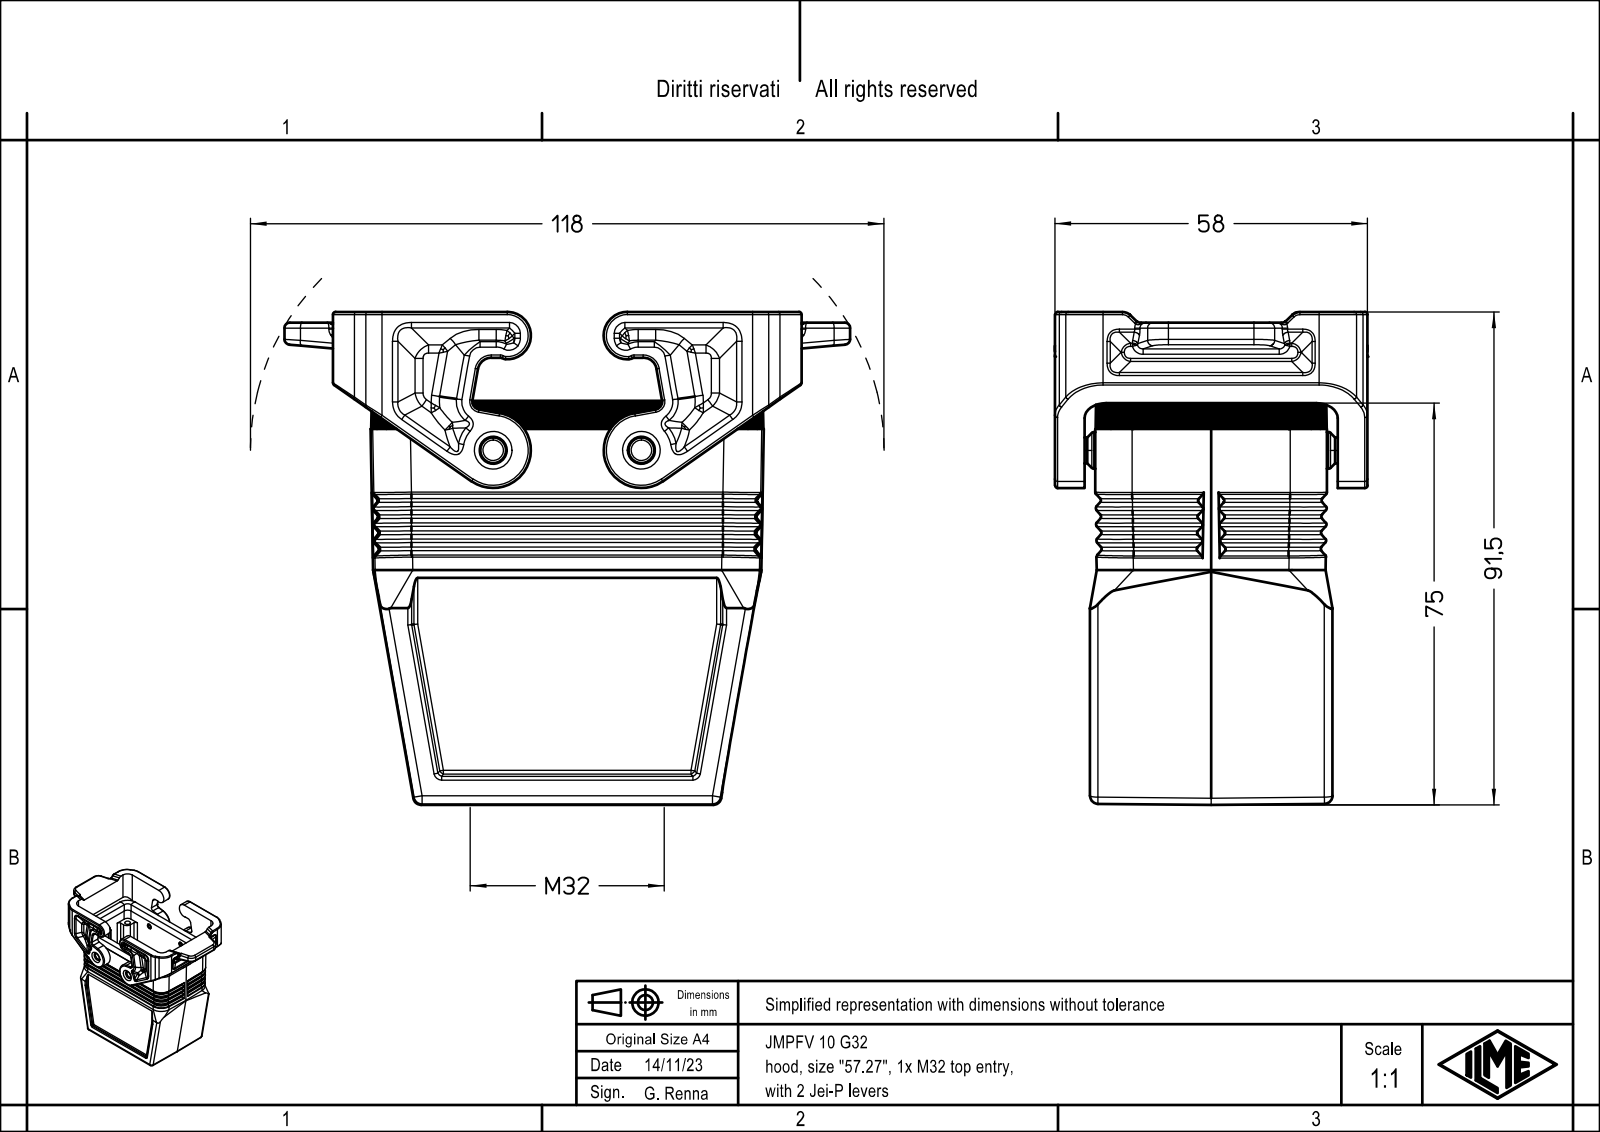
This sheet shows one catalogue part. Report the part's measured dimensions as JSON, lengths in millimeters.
{"part_name": "JMPFV 10 G32", "step_written_by": "Creo Elements/Direct Modeling 20.1B 02-Apr-2019 (C) Parametric Technology GmbH (AUTOMOTIVE_DESIGN)", "units": "millimeters", "bodies": {"solids": 1, "faces": 1097, "planar": 270, "cylindrical": 349, "other": 478}, "overall_size": [105, 91.45, 58.08], "volume_mm3": 96180, "surface_area_mm2": 47623, "round_holes": [[3, 4], [3.5, 4], [4.8, 2], [30.6, 1]], "round_bosses_or_shafts": [[6.8, 2]], "partial_cylinders_radius": [[0.5, 69], [1, 56], [3, 34], [1.5, 28], [2, 20], [0.33, 15], [7, 14], [4, 12]], "face_to_face_distances": [39.25, 2, 3.75, 5.75, 1, 45, 41.25, 43, 4.75, 40.25], "hole_center_spacings": [31.54, 27, 57, 63.07, 27.5]}
